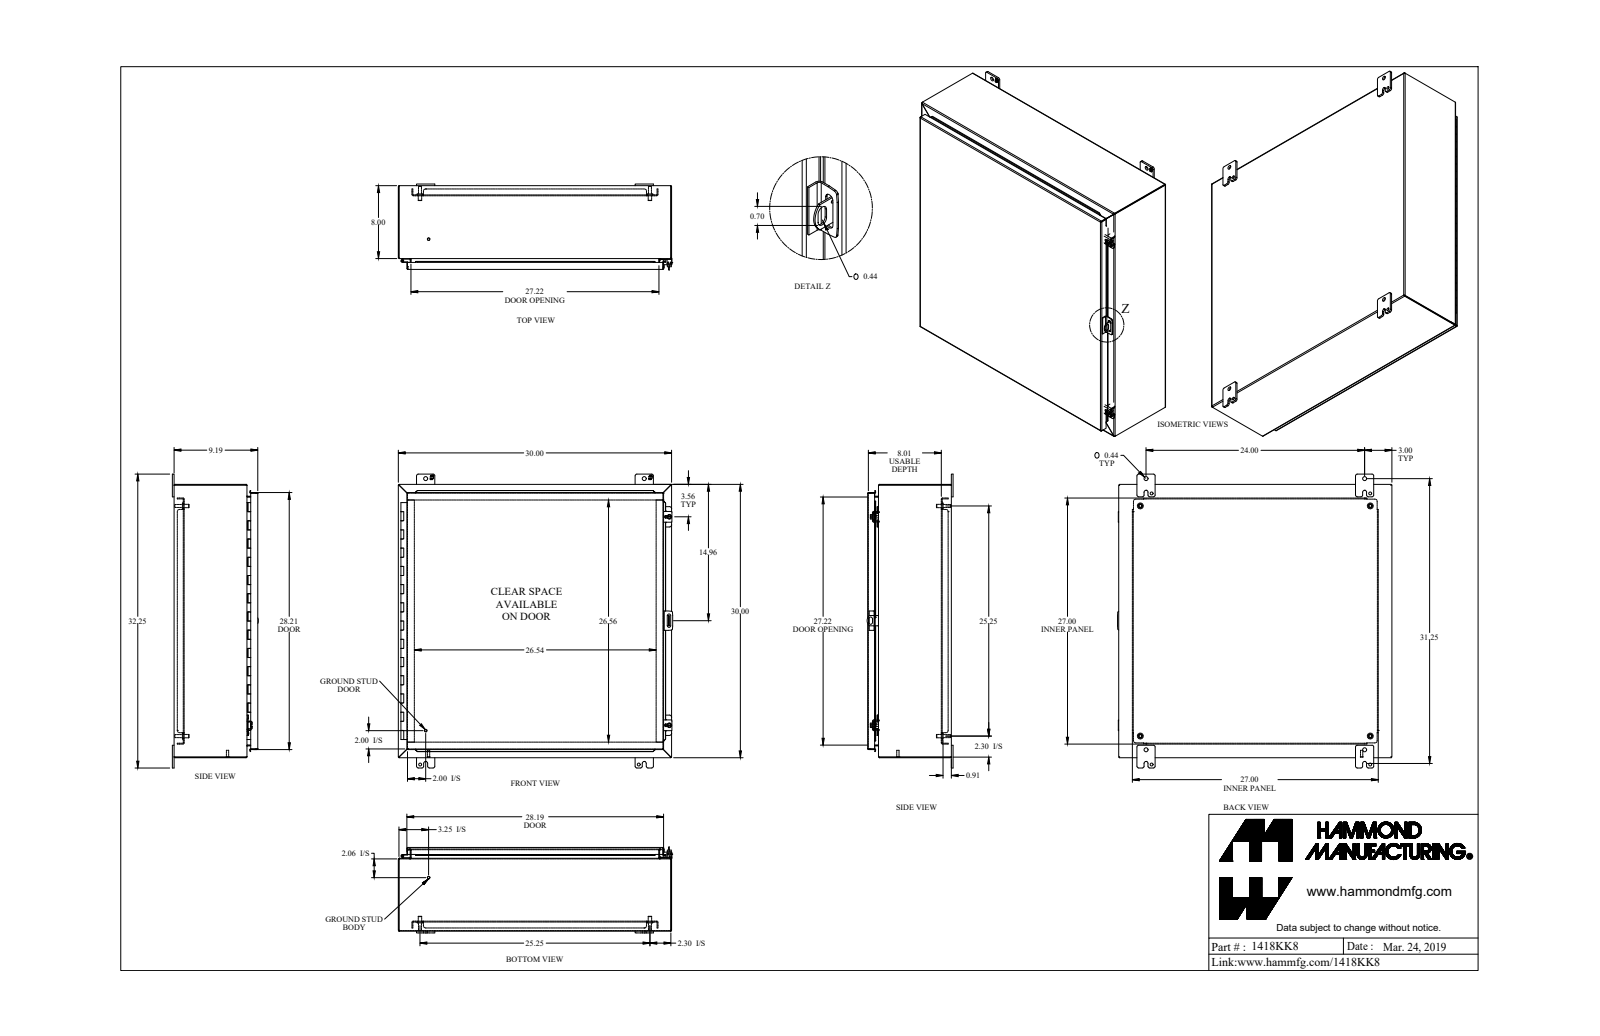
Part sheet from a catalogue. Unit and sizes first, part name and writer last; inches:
Units: inches
Overall size (bounding box): 32.25 × 30.125 × 9.437
Round holes (diameter × count): ⌀0.313 ×4, ⌀0.437 ×4, ⌀0.5 ×4, ⌀0.213 ×2, ⌀0.265 ×2, ⌀0.307 ×2, ⌀0.375 ×2, ⌀0.445 ×2, ⌀0.125 ×1, ⌀0.187 ×1
Round bosses / shafts (diameter × count): ⌀0.65 ×4, ⌀0.375 ×4, ⌀0.33 ×4, ⌀1 ×2, ⌀0.5 ×2, ⌀0.39 ×2, ⌀0.281 ×2, ⌀0.25 ×2
Partial cylindrical surfaces — rounded edges, fillets, slot ends (radius × count): R0.188 ×38, R0.036 ×24, R0.108 ×24, R0.25 ×16, R0.048 ×13, R0.143 ×13, R0.116 ×12, R0.045 ×8
Main face-to-face distances: 0.072, 9.113, 9.041, 29.928, 9.185, 0.095, 0.937, 1.009, 8.081, 8.009
Hole centre spacings: 25.25, 1.736, 24, 29.75, 35.709, 38.224, 36.359, 2.434
Volume: 332.6 in³ · Surface area: 8 617 in²
Bodies: 41 solids, 1311 faces (801 planar, 442 cylindrical, 68 other)
Part name (STEP PRODUCT): 1418KK8_Default
STEP written by: SolidWorks 2019 (CONFIG_CONTROL_DESIGN)
